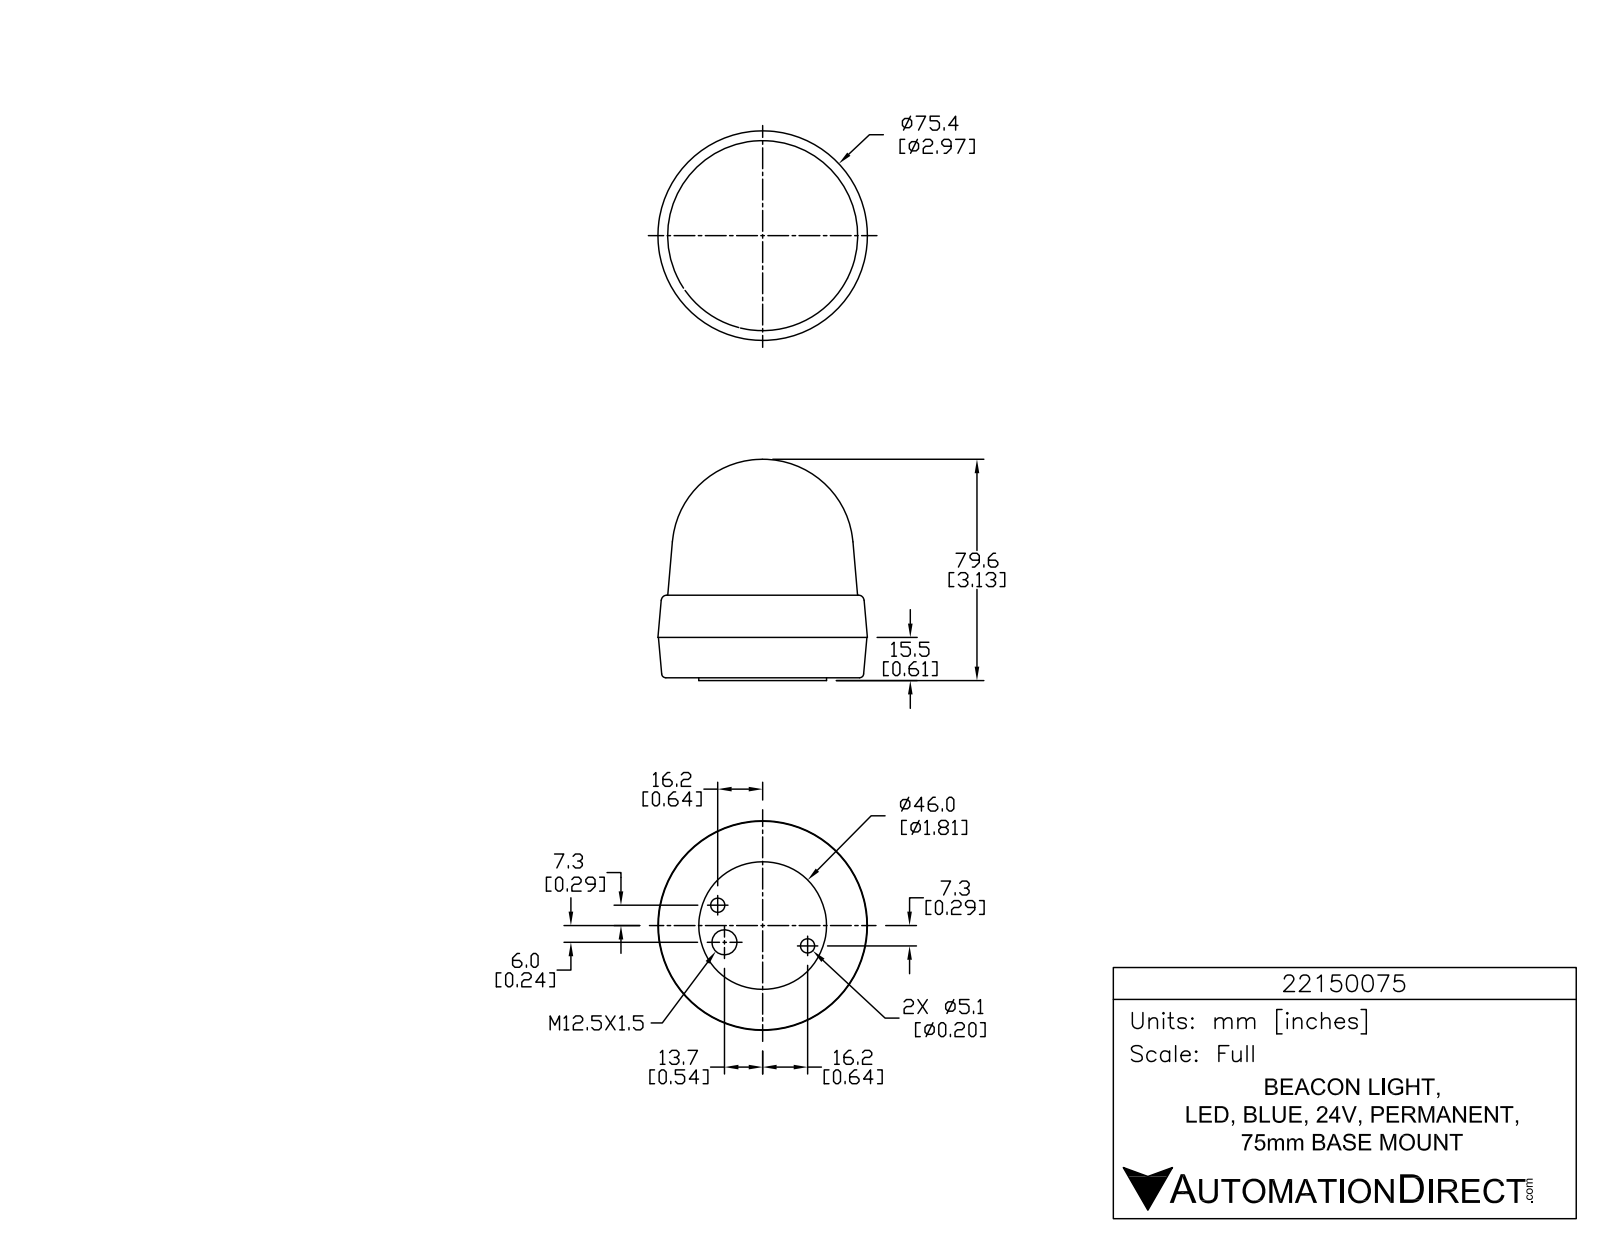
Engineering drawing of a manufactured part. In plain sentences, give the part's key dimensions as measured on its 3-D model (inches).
The part is named "22150075". Its 3-D file was written by "SolidWorks 2015 (AUTOMOTIVE_DESIGN)". It is 1 solid with 773 faces: 526 planar, 163 cylindrical and 84 other. Overall it measures 3.133 by 2.967 by 2.967 inches. Its volume is 15.79 cubic inches and its surface area 33.7 square inches. Round holes: 3 of diameter 0.059, 2 of diameter 0.201, 1 of diameter 0.354. Round bosses or shafts: 3 of diameter 0.339, 3 of diameter 0.084, 1 of diameter 1.811. Partial cylindrical surfaces (rounded edges, fillets, slot ends): 9 of radius 0.005, 6 of radius 0.005, 6 of radius 0.012, 6 of radius 0.012, 6 of radius 0.012, 6 of radius 0.196, 3 of radius 0.005, 3 of radius 0.005. The main face-to-face distances are 0.039, 1.209, 1.17, 0.61, 0.571, 0.599, 1.566, 1.527, 0.956, 0.357. The hole center spacings are 0.534, 1.179, 1.398.
